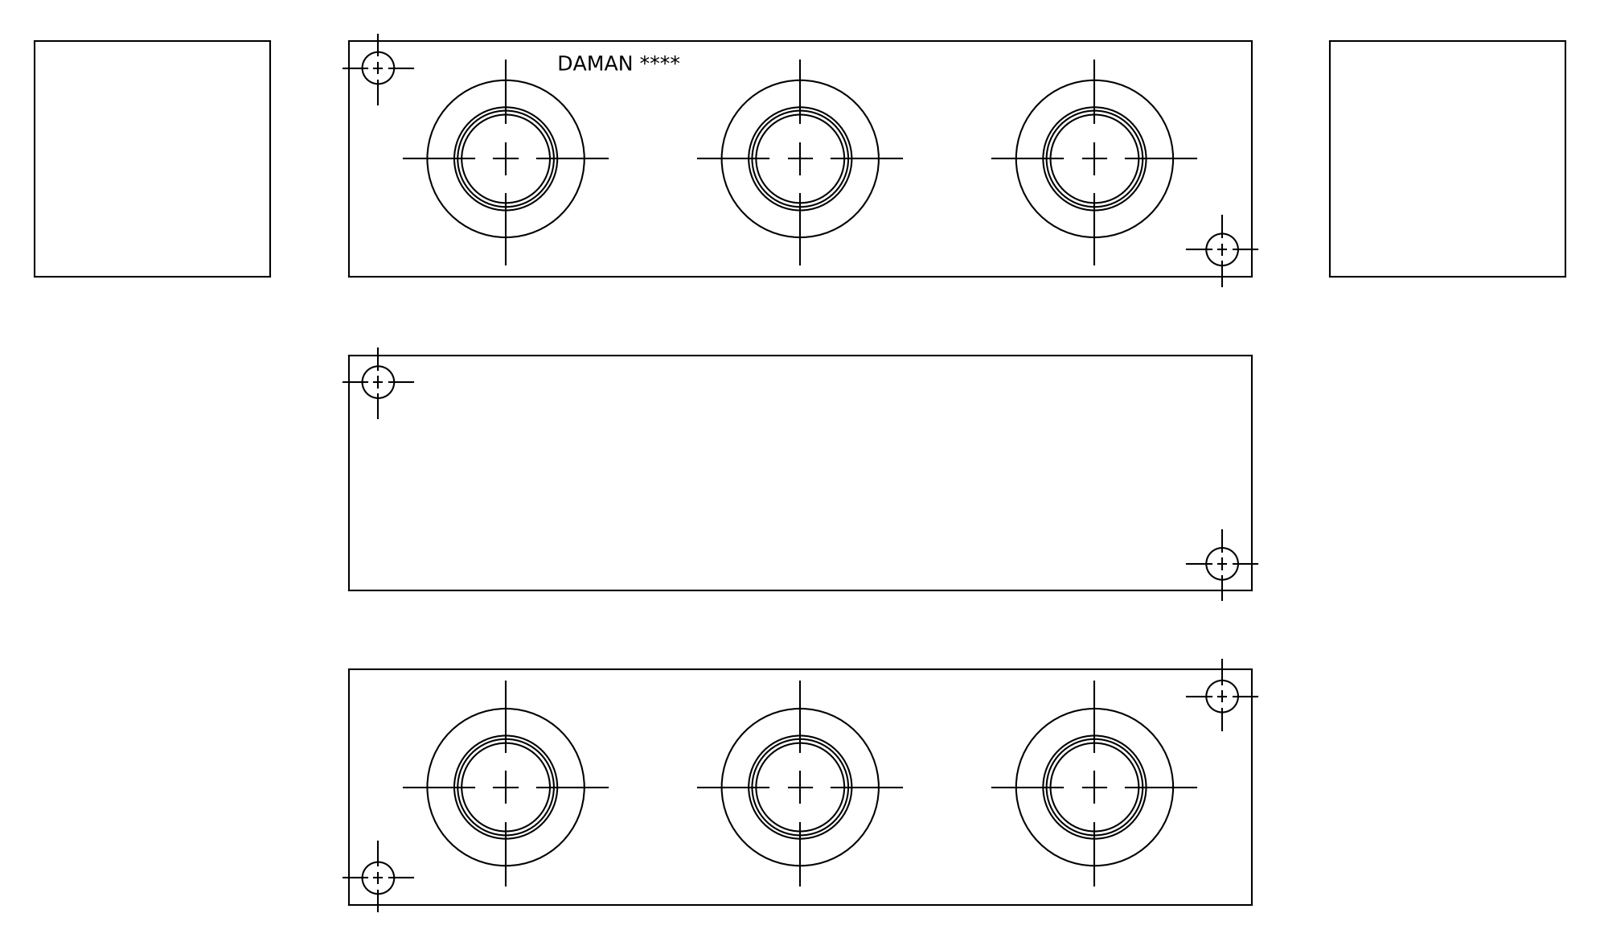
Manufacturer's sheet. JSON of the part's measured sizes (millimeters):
{"part_name": "Part_+J1800316S_3D", "step_written_by": "Autodesk Inventor 2020 (AUTOMOTIVE_DESIGN)", "units": "millimeters", "bodies": {"solids": 1, "faces": 418, "planar": 229, "cylindrical": 43, "other": 146}, "overall_size": [292.1, 76.2, 76.2], "volume_mm3": 1498000, "surface_area_mm2": 127794, "round_holes": [[10.31, 4], [28.57, 3], [31.27, 3], [33.35, 3], [33.76, 3], [35.51, 3], [49.12, 3], [33.34, 1]], "face_to_face_distances": [76.2, 292.1, 0.79, 75.41, 74.62, 19.84, 56.36, 19.05, 55.57, 36.52], "hole_center_spacings": [50.65, 95.25, 139.64, 233.62, 279.28, 190.5]}
